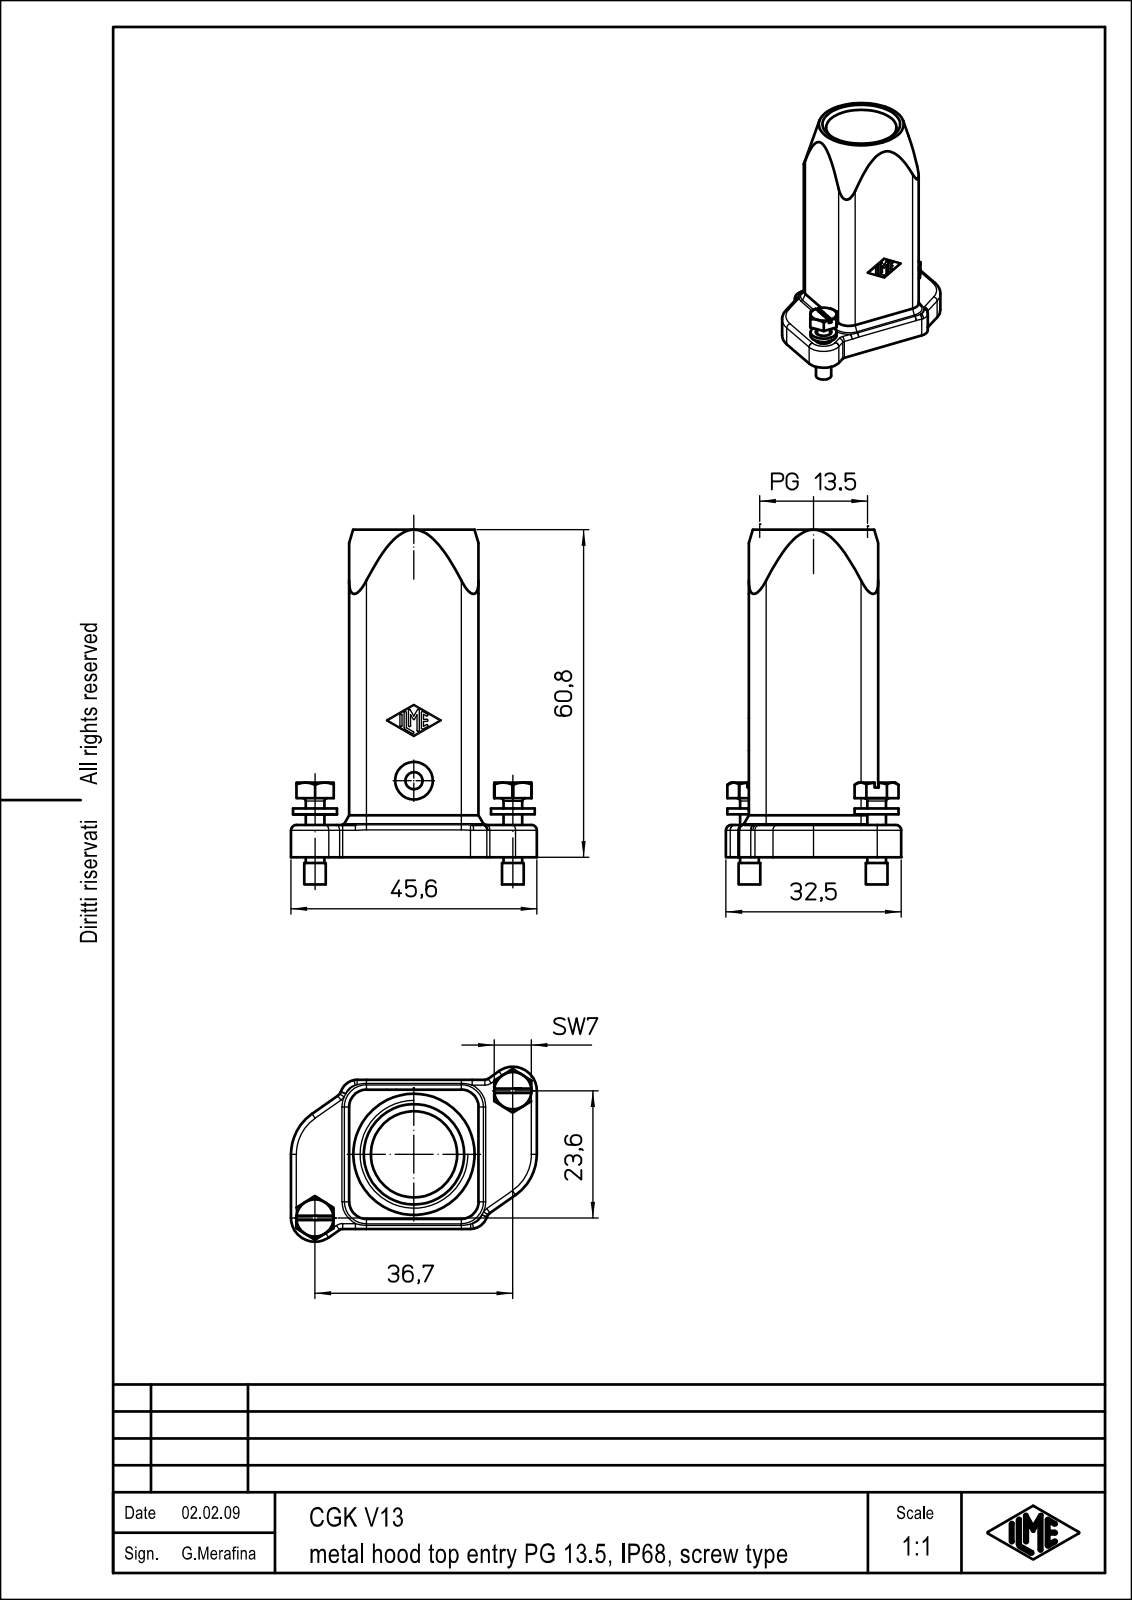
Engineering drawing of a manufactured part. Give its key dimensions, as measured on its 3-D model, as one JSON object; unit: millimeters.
{"part_name": "53813", "step_written_by": "CoCreate Modeling 16.00A 16-Aug-2008 (C) Parametric Technology GmbH (AUTOMOTIVE_DESIGN)", "units": "millimeters", "bodies": {"solids": 1, "faces": 182, "planar": 89, "cylindrical": 72, "other": 21}, "overall_size": [60.8, 45.6, 32.5], "volume_mm3": 11212, "surface_area_mm2": 12369, "round_holes": [[4.2, 2], [3.2, 1], [7, 1], [16, 1]], "partial_cylinders_radius": [[0.2, 11], [3.2, 6], [0.5, 4], [2, 4], [4.7, 4], [0.1, 3], [0.16, 2], [1, 2]], "face_to_face_distances": [24, 2, 1.85, 25.85, 4, 6, 1.82, 41.3, 43.3, 47.3], "hole_center_spacings": [21.82, 43.63]}
